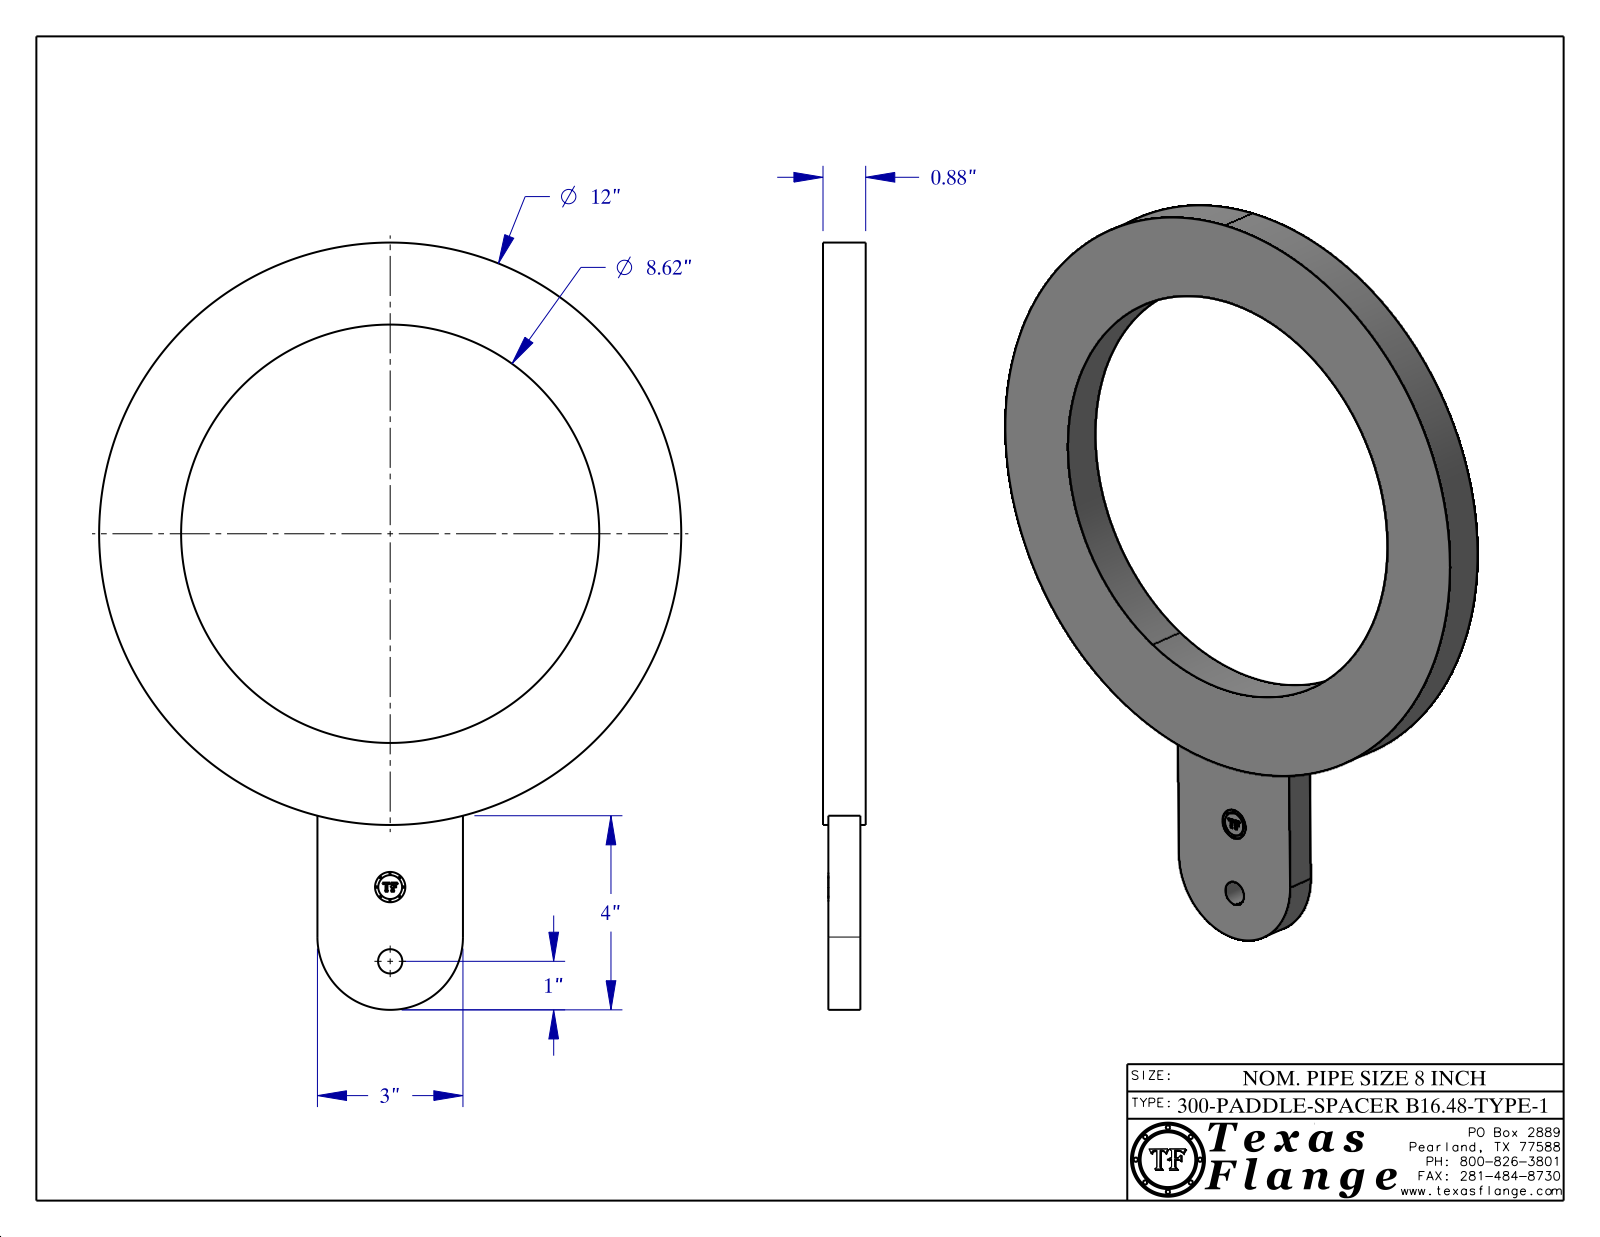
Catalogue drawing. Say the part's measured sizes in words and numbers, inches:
The part is named "8-300-PADDLE-SPACER-B16.48-TYPE-2". Its 3-D file was written by "CATIA V5 STEP AP214 (AUTOMOTIVE_DESIGN)". It is 1 solid with 398 faces: 371 planar, 27 cylindrical and 0 other. Overall it measures 15.809 by 12 by 0.88 inches. Its volume is 55.07 cubic inches and its surface area 193 square inches. Round holes: 1 of diameter 0.5, 1 of diameter 0.625, 1 of diameter 8.62. Round bosses or shafts: 8 of diameter 0.038, 1 of diameter 12, 1 of diameter 0.492. Partial cylindrical surfaces (rounded edges, fillets, slot ends): 1 of radius 1.5. The main face-to-face distances are 0.88, 0.11, 0.77, 0.66, 3, 0.755, 0.645, 0.015, 0.125, 1.437. The hole center spacings are 1.53, 7.28, 8.809.
